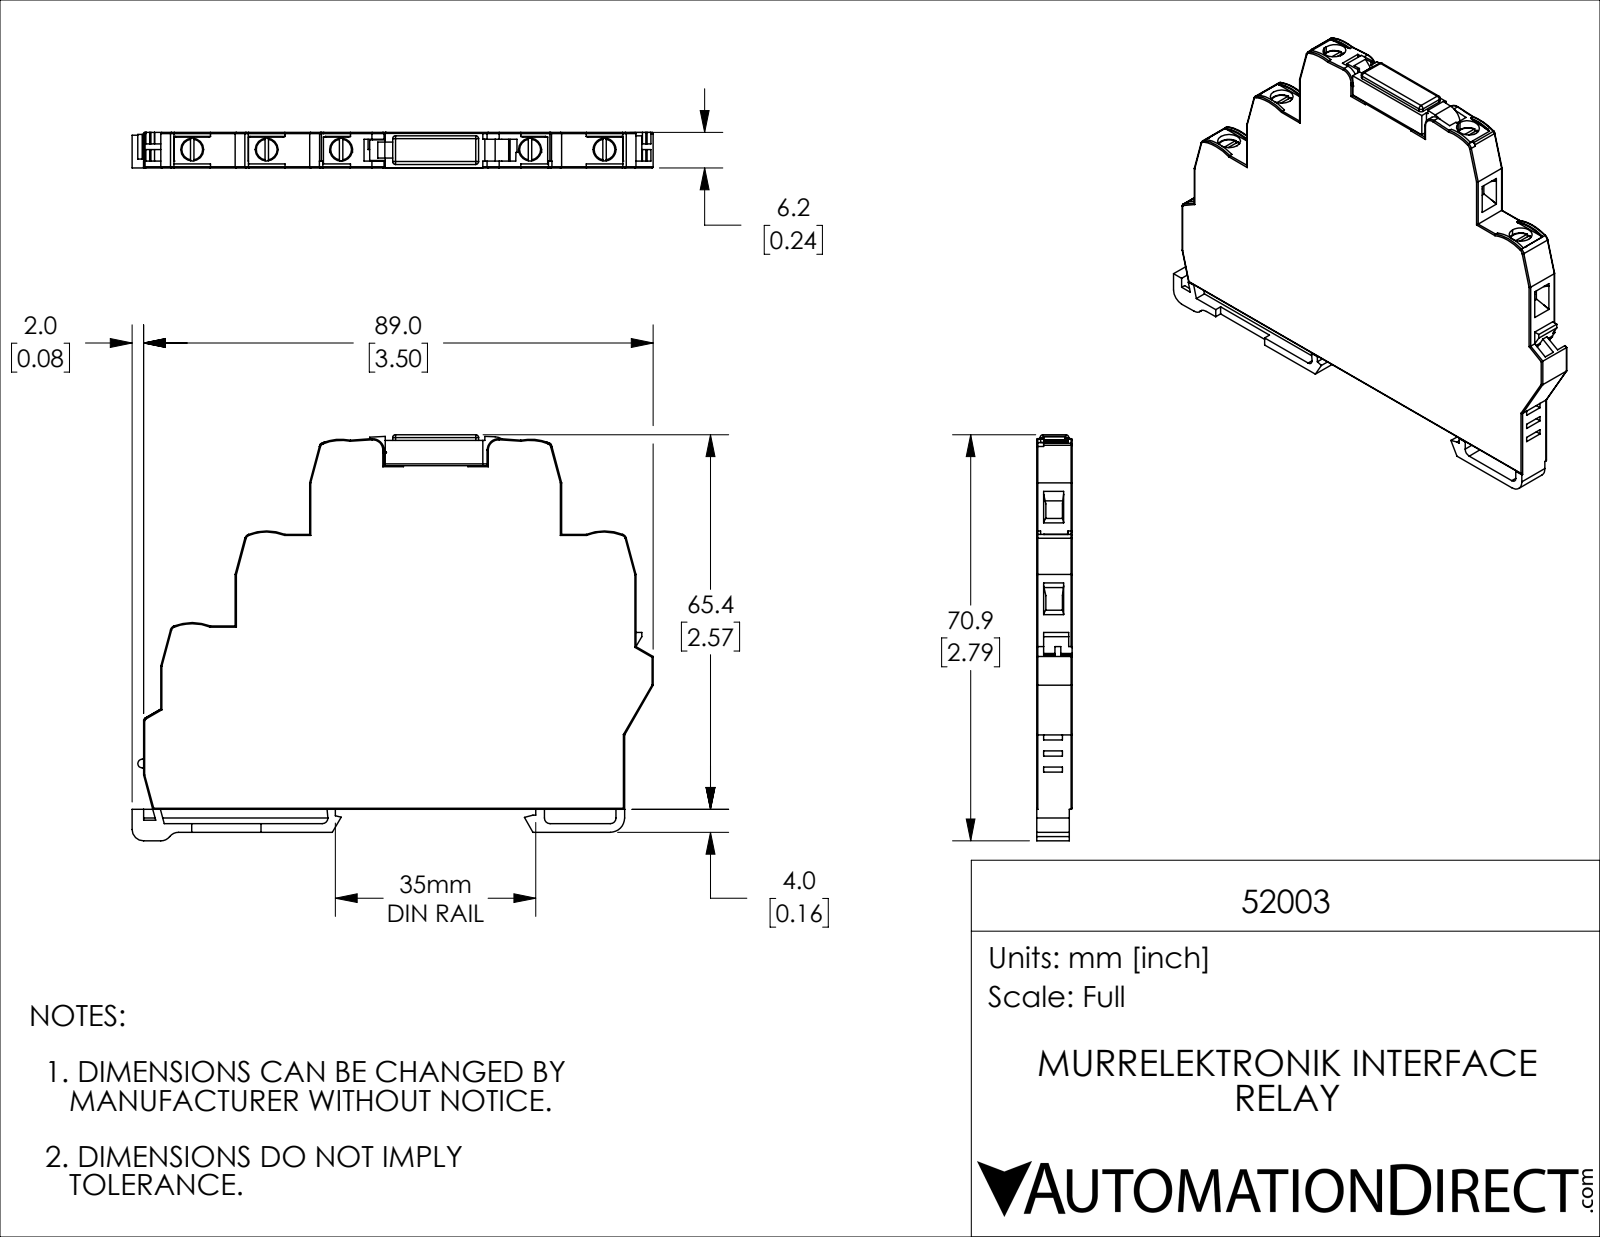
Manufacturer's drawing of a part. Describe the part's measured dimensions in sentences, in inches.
The part is named "52003". Its 3-D file was written by "SolidWorks 2019 (CONFIG_CONTROL_DESIGN)". It is 2 solids with 566 faces: 351 planar, 147 cylindrical and 68 other. Overall it measures 3.583 by 2.791 by 0.244 inches. Its volume is 1.706 cubic inches and its surface area 20.13 square inches. Round holes: 5 of diameter 0.157, 1 of diameter 0.075. Round bosses or shafts: 1 of diameter 0.079. Partial cylindrical surfaces (rounded edges, fillets, slot ends): 56 of radius 0.008, 11 of radius 0.02, 8 of radius 0.039, 6 of radius 0.079, 5 of radius 0.03, 5 of radius 0.346, 4 of radius 0.005, 3 of radius 0.016. The main face-to-face distances are 0.244, 0.059, 0.197, 0.098, 0.157, 0.118, 0.047, 0.02, 0.039, 2.362. The hole center spacings are 0.512, 1.811, 2.323, 1.024, 1.299, 2.835.
